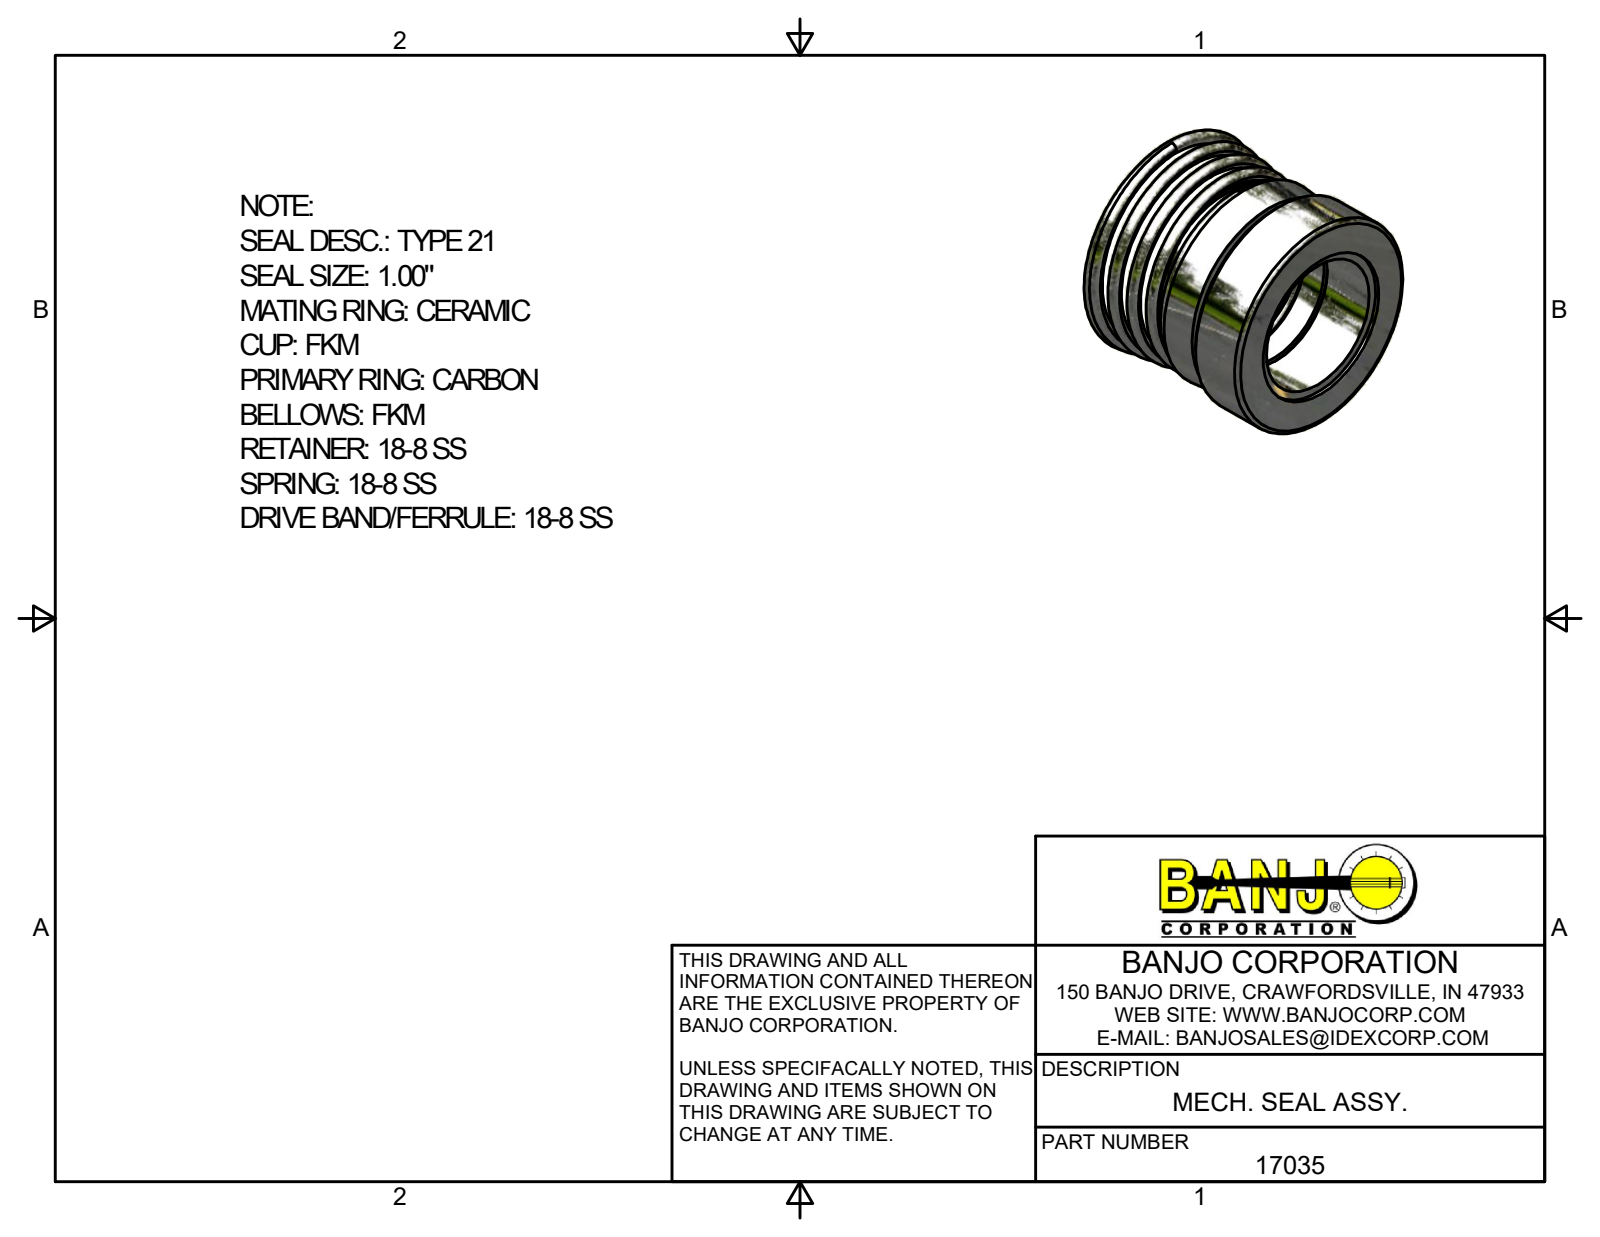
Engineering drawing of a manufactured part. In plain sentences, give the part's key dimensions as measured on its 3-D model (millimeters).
The part is named "17035". Its 3-D file was written by "Autodesk Inventor 2017 (AUTOMOTIVE_DESIGN)". It is 4 solids with 73 faces: 30 planar, 26 cylindrical and 17 other. Overall it measures 42.22 by 42.22 by 38.07 millimeters. Round holes: 1 of diameter 25.4, 1 of diameter 26.99, 1 of diameter 28.57. Round bosses or shafts: 1 of diameter 41.27, 1 of diameter 39.69, 1 of diameter 33.34, 1 of diameter 33.07, 1 of diameter 31.75, 1 of diameter 28.45. The main face-to-face distances are 11.11, 12.7, 19.05, 7.94, 6.35, 1.59, 0.79, 4.76, 10.32, 23.81.
